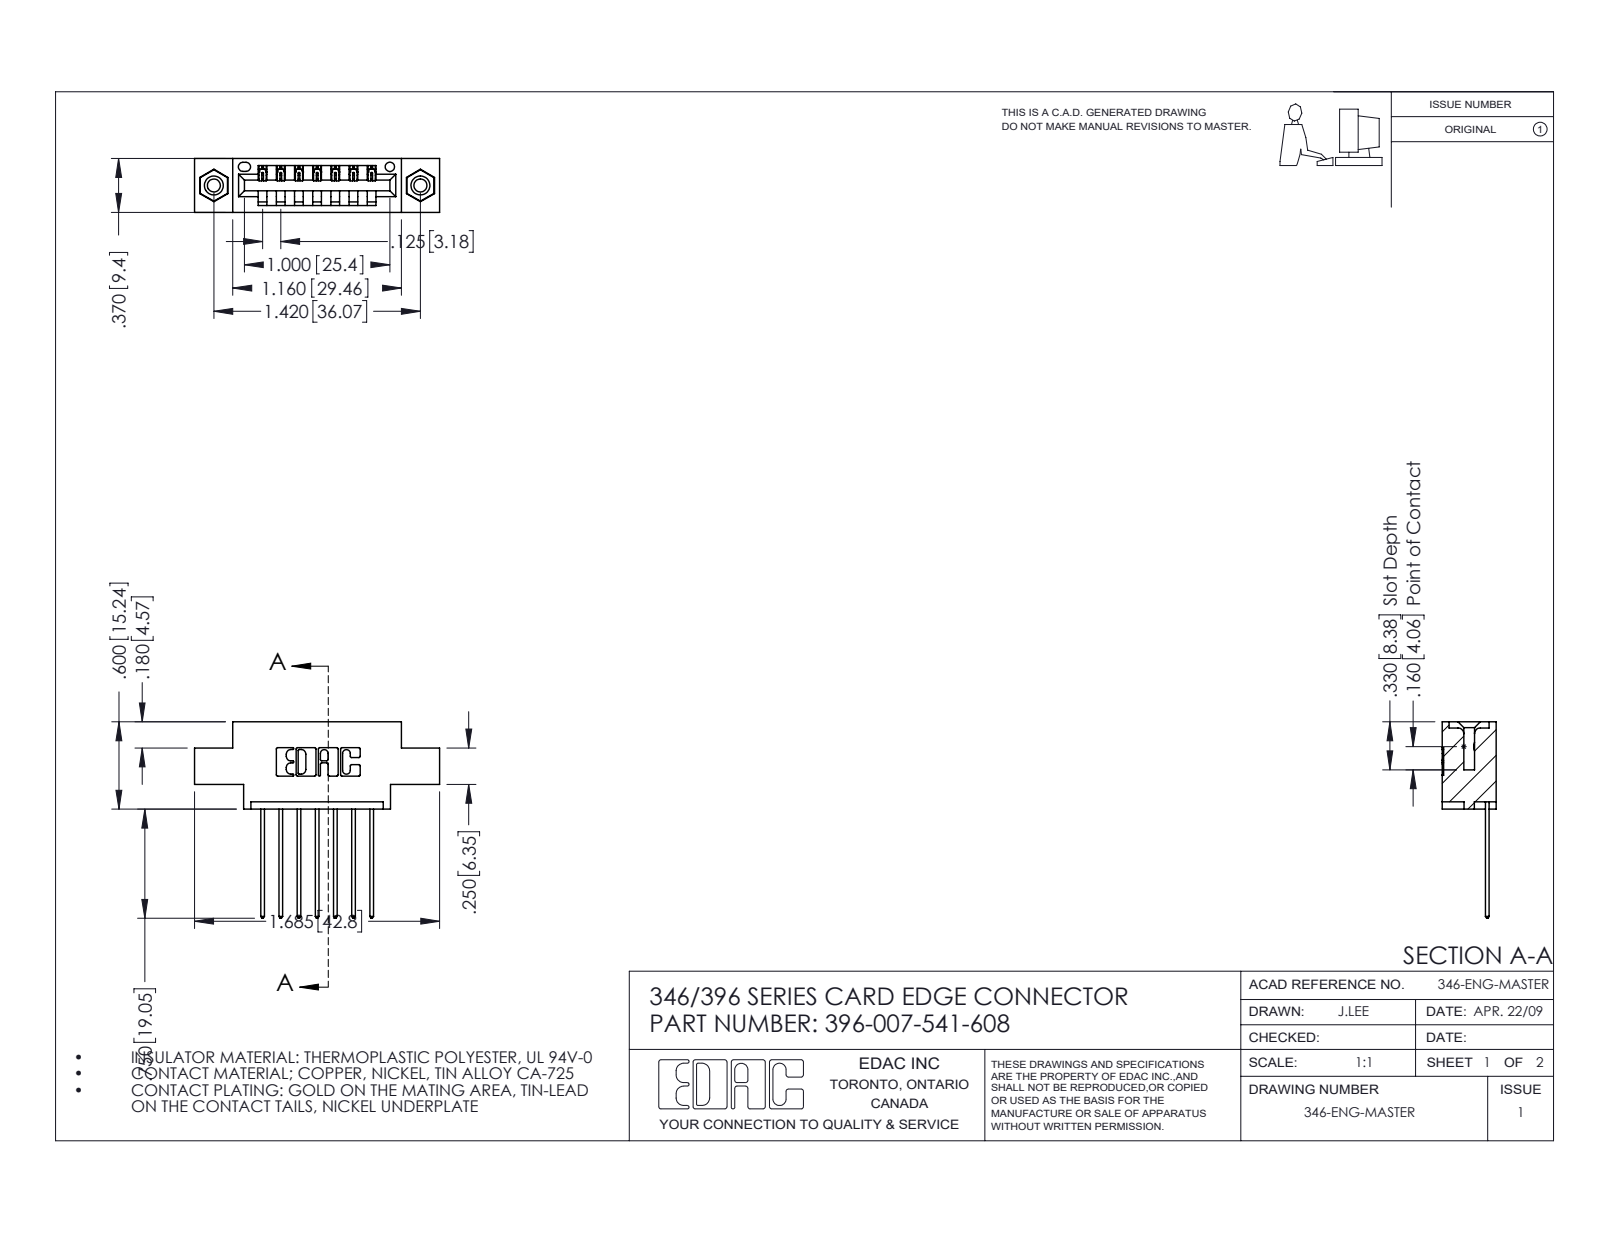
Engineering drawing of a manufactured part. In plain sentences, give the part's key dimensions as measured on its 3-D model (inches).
The part is named "345-250-001_345-250-003-102; 396-007-541-608; 345-292-001_345-293-141; 346 Part_0.170 Offset - 0.156 Dia-TI". Its 3-D file was written by "SolidWorks 2016 (CONFIG_CONTROL_DESIGN)". It is 10 solids with 592 faces: 392 planar, 184 cylindrical and 16 other. Overall it measures 1.685 by 1.35 by 0.37 inches. Its volume is 0.227 cubic inches and its surface area 7.113 square inches. Round holes: 2 of diameter 0.089, 2 of diameter 0.125, 2 of diameter 0.156, 1 of diameter 0.064. Round bosses or shafts: 2 of diameter 0.155. Partial cylindrical surfaces (rounded edges, fillets, slot ends): 22 of radius 0.01, 14 of radius 0.006, 14 of radius 0.01, 6 of radius 0.007, 6 of radius 0.031, 3 of radius 0.026, 2 of radius 0.031, 2 of radius 0.04. The main face-to-face distances are 0.25, 0.37, 0.048, 0.322, 0.072, 0.298, 0.025, 0.222, 0.148, 0.1. The hole center spacings are 0.246, 1.217, 1.42.
